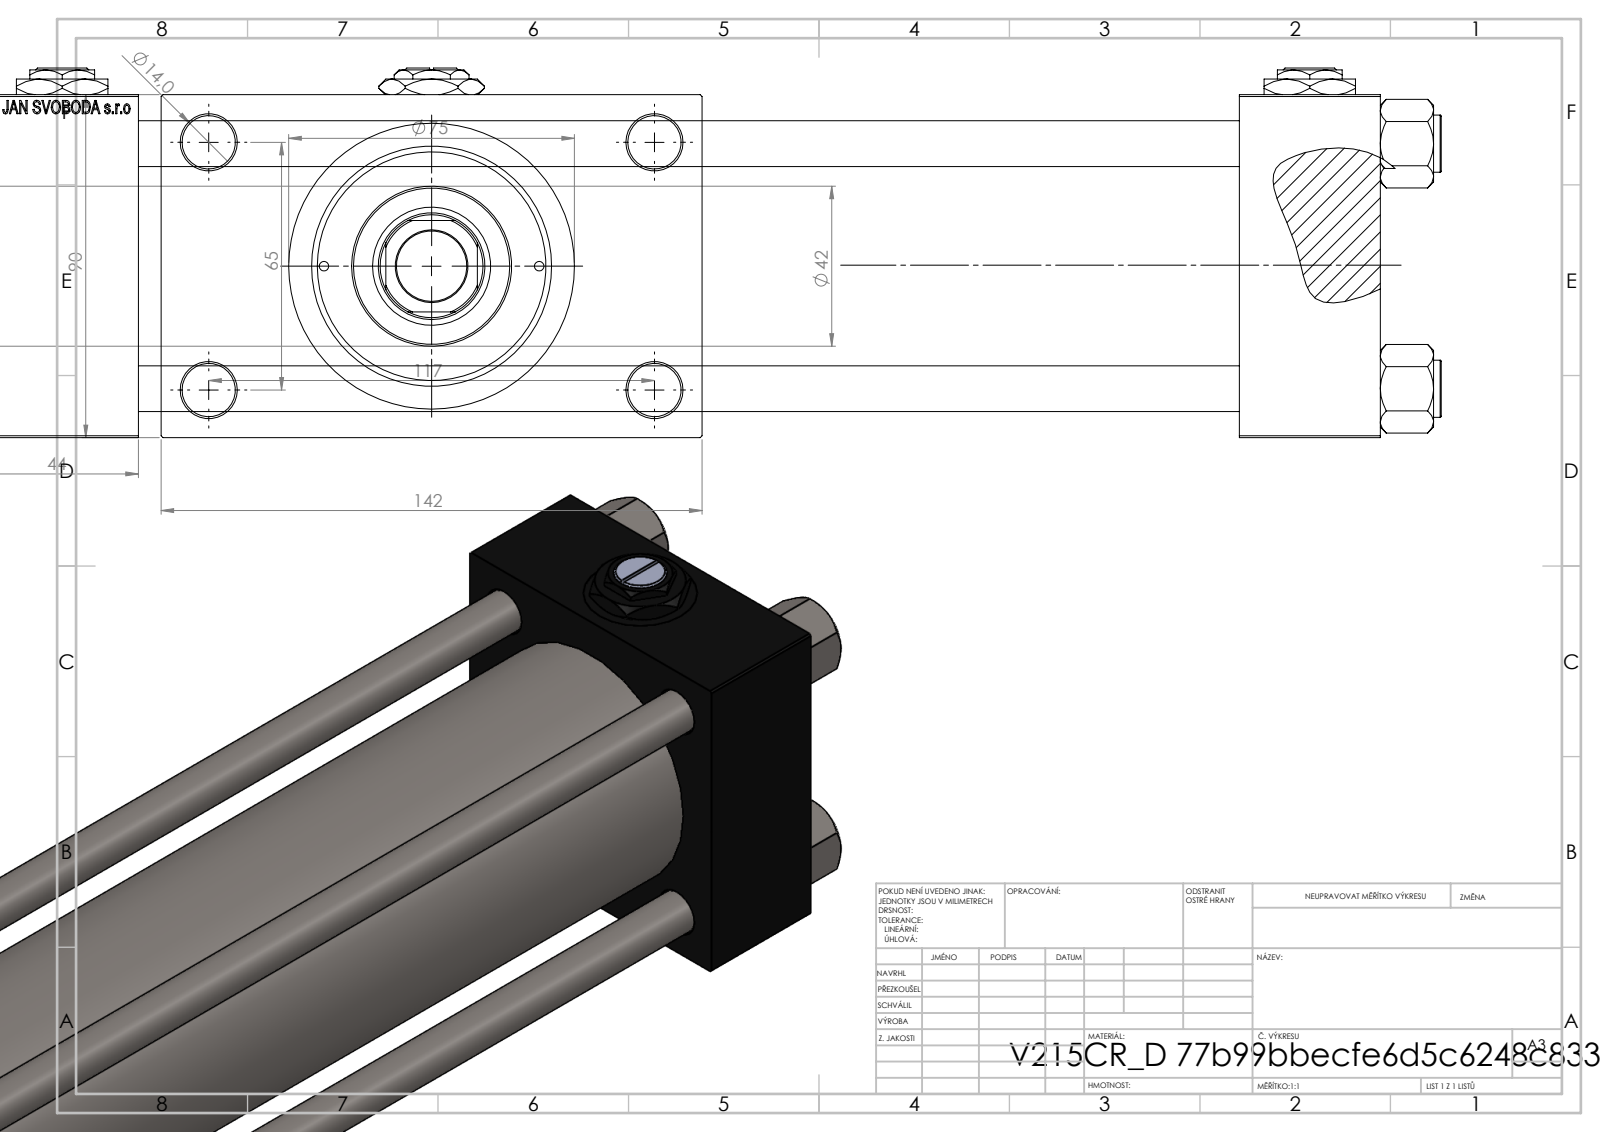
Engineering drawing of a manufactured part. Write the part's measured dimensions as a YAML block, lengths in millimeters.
part_name: "NUT_M5_D; V215CR_D_TYCINKA; V215_VC_A; V215CR_D_Body (+2 more)"
step_written_by: "SolidWorks 2019 (CONFIG_CONTROL_DESIGN)"
units: millimeters
bodies: {solids: 13, faces: 1212, planar: 547, cylindrical: 103, other: 562}
overall_size: [433, 142, 97]
volume: 1479000
surface_area: 355151
round_holes:
  - {diameter: 12, count: 4}
  - {diameter: 14, count: 4}
  - {diameter: 20.96, count: 4}
  - {diameter: 30, count: 4}
  - {diameter: 7, count: 3}
  - {diameter: 2.5, count: 2}
  - {diameter: 18.5, count: 1}
  - {diameter: 28, count: 1}
  - {diameter: 31, count: 1}
  - {diameter: 50, count: 1}
  - {diameter: 60, count: 1}
  - {diameter: 63, count: 1}
round_bosses_or_shafts:
  - {diameter: 15, count: 4}
  - {diameter: 75, count: 1}
  - {diameter: 69, count: 1}
  - {diameter: 42, count: 1}
partial_cylinders:
  - {radius: 13.5, count: 1}
face_to_face_distances: [90, 289, 37, 326, 333, 370, 44, 26, 116, 16]
hole_center_spacings: [26.35, 32.39, 44.4, 45.47, 64.3, 66.92, 68.42, 69.81]
